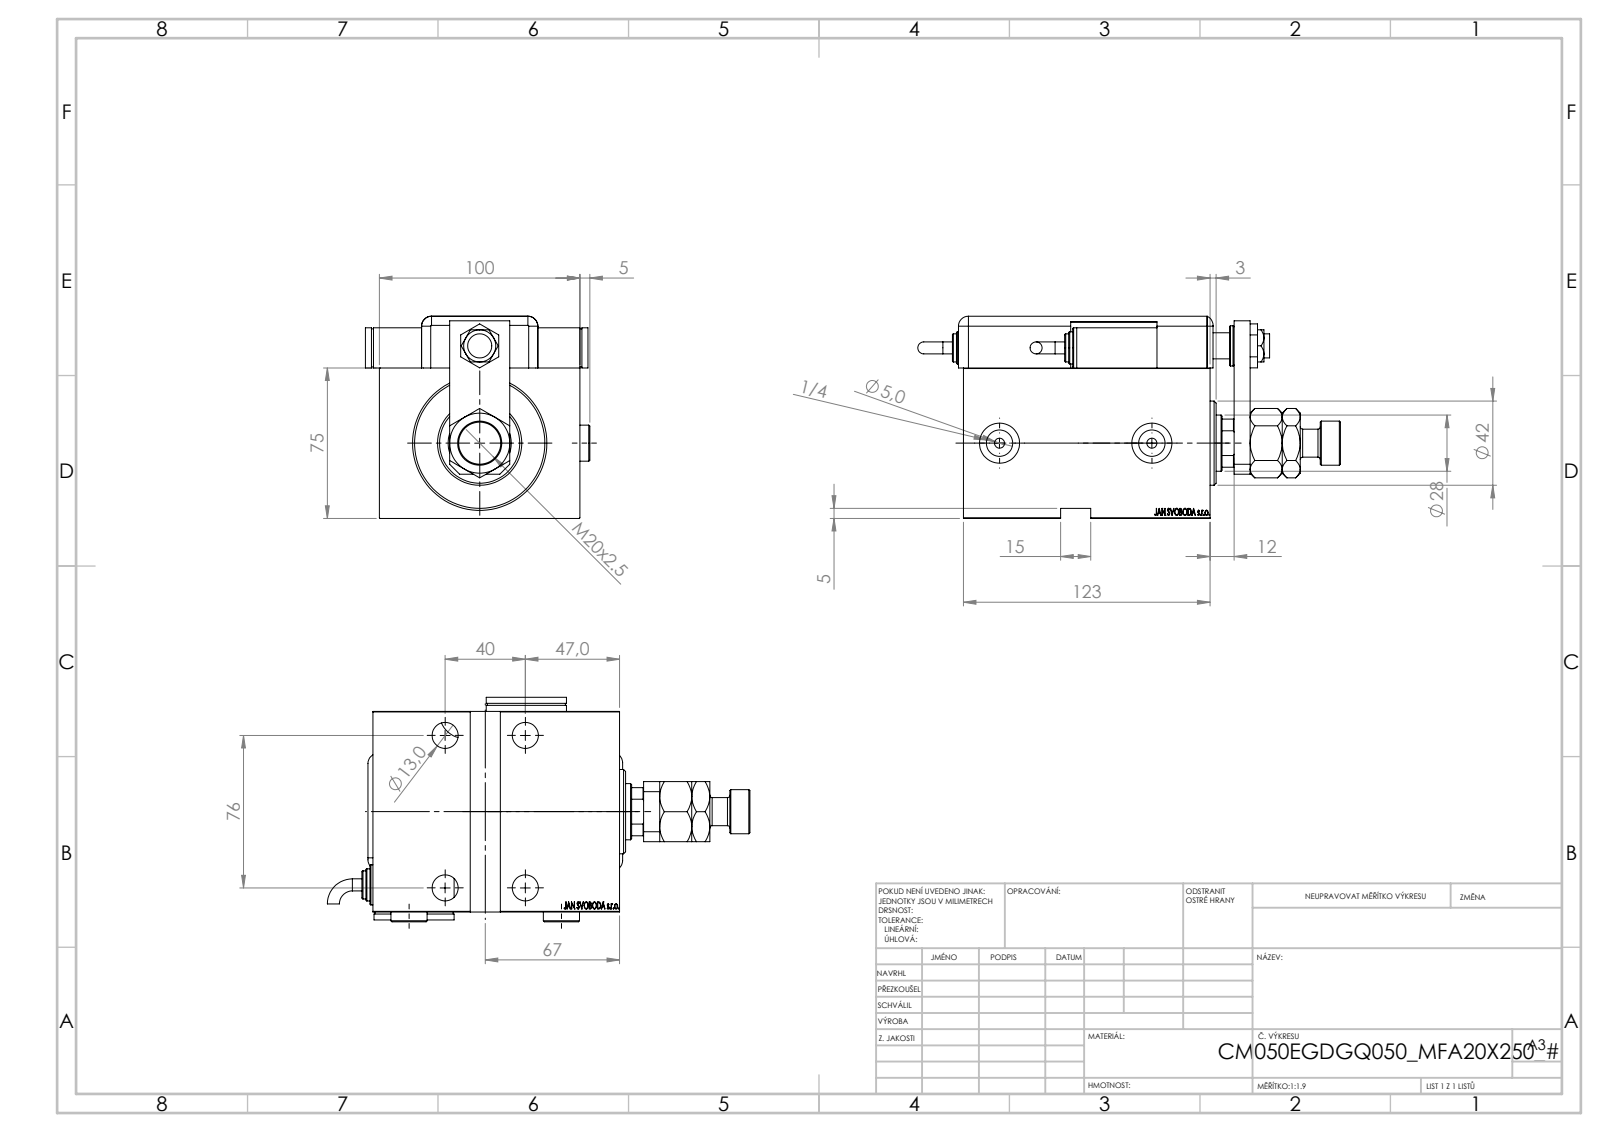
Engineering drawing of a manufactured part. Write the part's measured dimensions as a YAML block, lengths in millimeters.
part_name: "Q_T_W_MFA; V450CM_E_VCP; SWITCH DIM A_G; Zatka_OIL_PORT (+7 more)"
step_written_by: "SolidWorks 2019 (CONFIG_CONTROL_DESIGN)"
units: millimeters
bodies: {solids: 16, faces: 1348, planar: 668, cylindrical: 127, other: 553}
overall_size: [210.76, 111.9, 100.8]
volume: 976257
surface_area: 189107
round_holes:
  - {diameter: 13, count: 5}
  - {diameter: 19, count: 4}
  - {diameter: 20, count: 3}
  - {diameter: 4, count: 2}
  - {diameter: 5, count: 2}
  - {diameter: 8, count: 2}
  - {diameter: 13.16, count: 2}
  - {diameter: 12, count: 1}
  - {diameter: 14, count: 1}
  - {diameter: 18.5, count: 1}
  - {diameter: 28, count: 1}
  - {diameter: 31.5, count: 1}
round_bosses_or_shafts:
  - {diameter: 20, count: 3}
  - {diameter: 14, count: 3}
  - {diameter: 18, count: 2}
  - {diameter: 16, count: 2}
  - {diameter: 6, count: 2}
  - {diameter: 52, count: 1}
  - {diameter: 42, count: 1}
  - {diameter: 22, count: 1}
partial_cylinders:
  - {radius: 5, count: 9}
  - {radius: 10, count: 1}
  - {radius: 13.5, count: 1}
face_to_face_distances: [3, 75, 100, 14, 20, 123, 100.8, 25.8, 109, 25]
hole_center_spacings: [76, 40, 47.2, 61.22, 82.87, 85.88, 91.59, 20]
